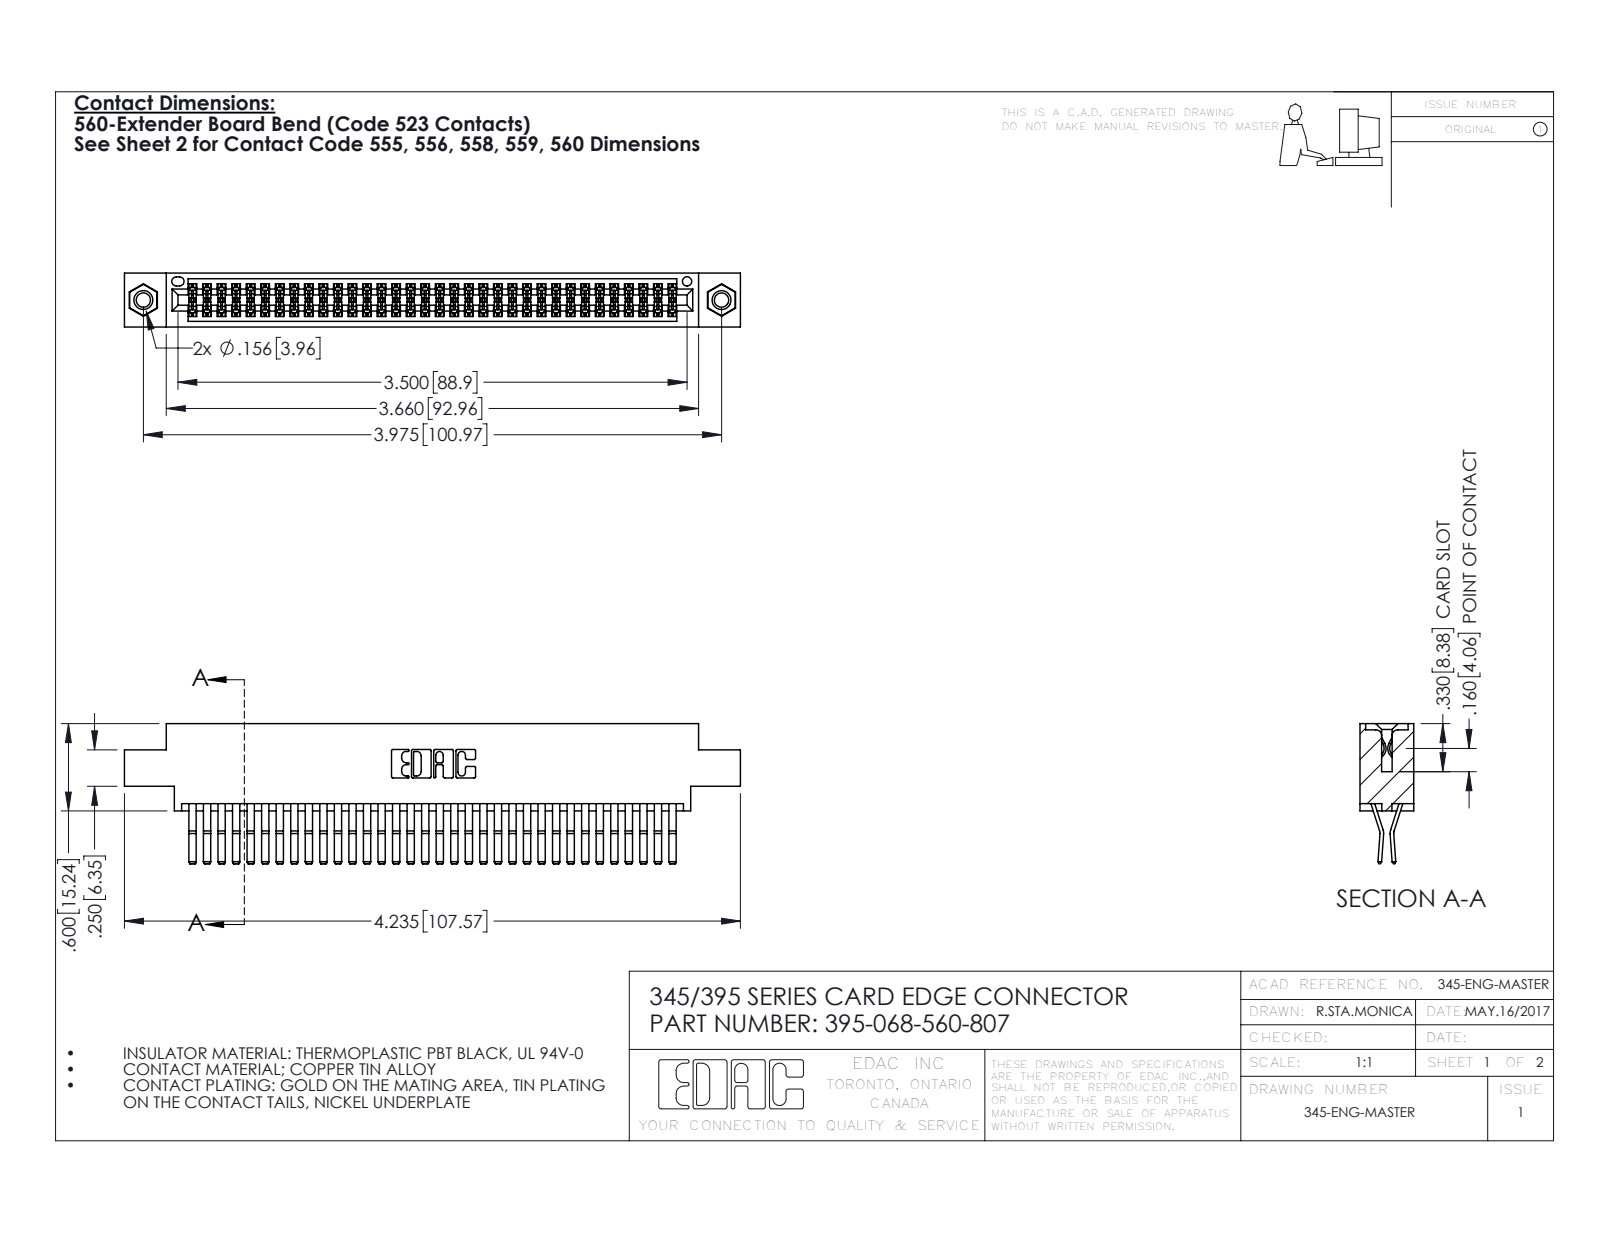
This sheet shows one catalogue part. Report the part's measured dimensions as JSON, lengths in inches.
{"part_name": "395-068-560-807; 345-250-001_345-250-005-103; 345 Part_0.170 Offset - 0.156 Dia-TI; 345-292-001_560 Tail", "step_written_by": "SolidWorks 2016 (CONFIG_CONTROL_DESIGN)", "units": "inches", "bodies": {"solids": 71, "faces": 3726, "planar": 2360, "cylindrical": 1350, "other": 16}, "overall_size": [4.235, 0.962, 0.37], "volume_in3": 0.653, "surface_area_in2": 26.3, "round_holes": [[0.098, 2], [0.125, 2], [0.156, 2], [0.064, 1]], "round_bosses_or_shafts": [[0.155, 2]], "partial_cylinders_radius": [[0.006, 102], [0.01, 22], [0.007, 6], [0.031, 6], [0.026, 3], [0.01, 2], [0.014, 2], [0.019, 2]], "face_to_face_distances": [0.025, 0.072, 0.298, 0.37, 0.2, 0.098, 0.272, 0.225, 0.175, 0.149], "hole_center_spacings": [0.27, 3.74, 3.975]}
